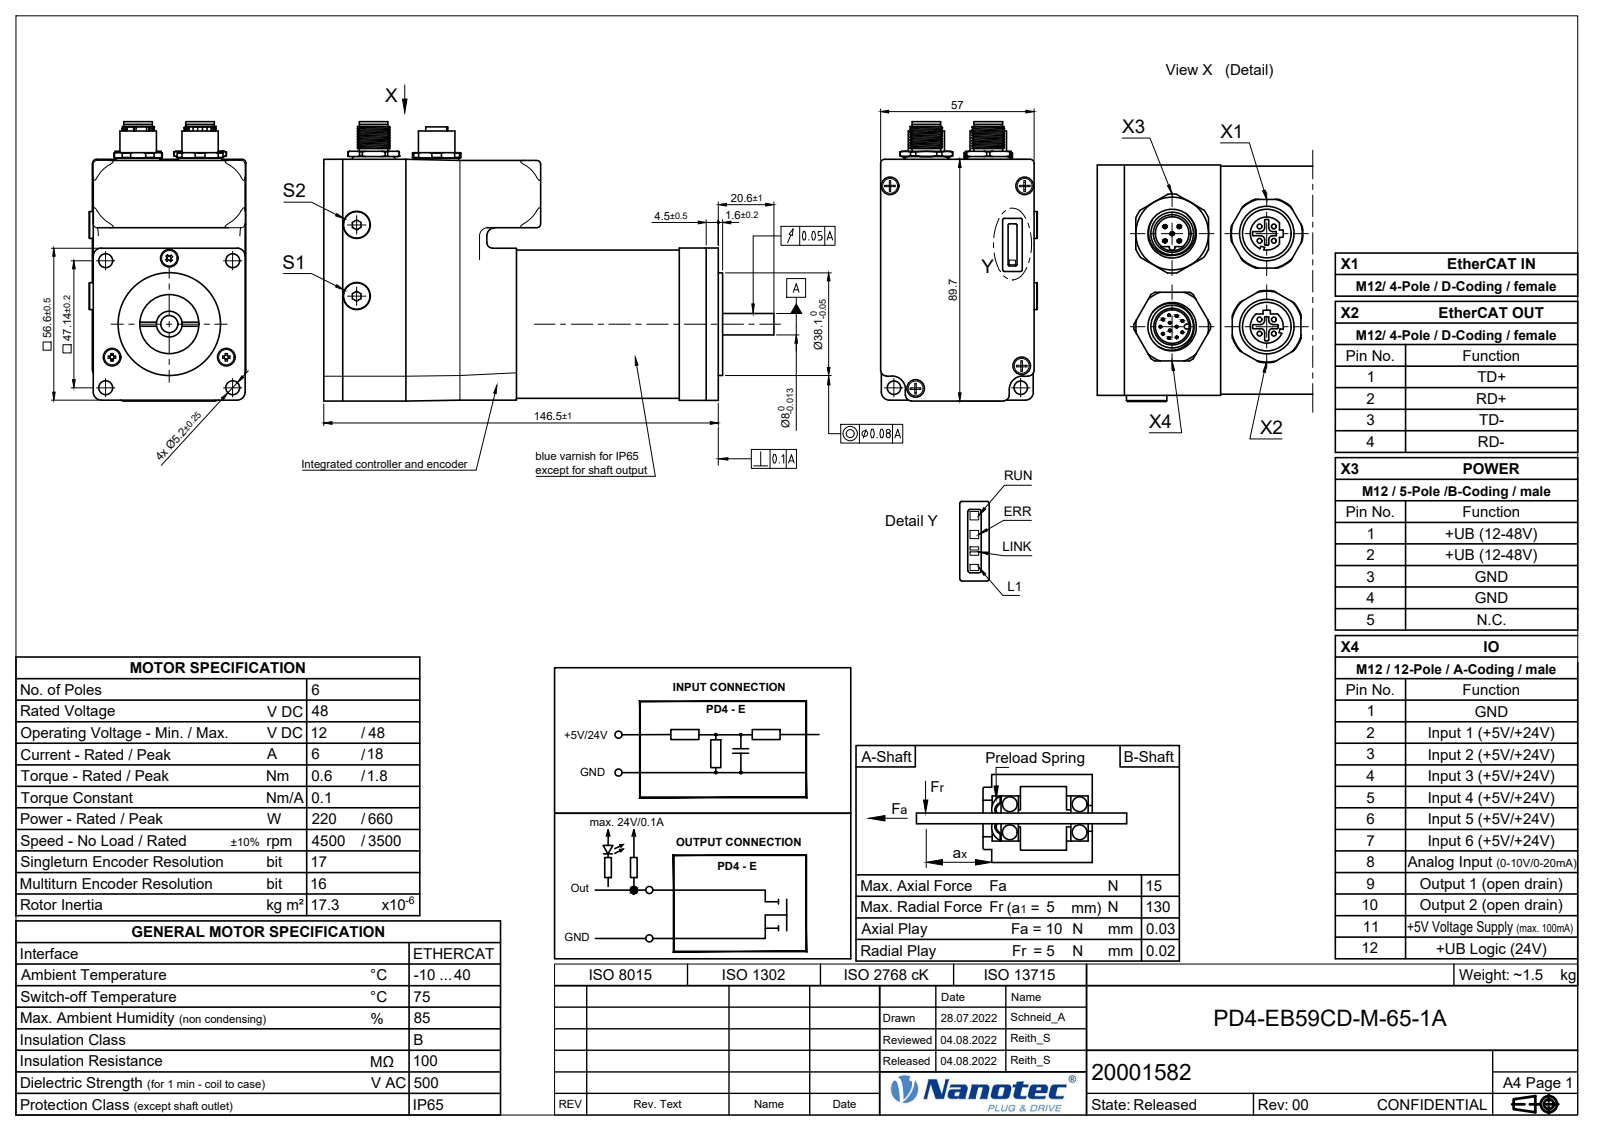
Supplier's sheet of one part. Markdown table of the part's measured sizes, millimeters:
| quantity | value |
| --- | --- |
| part name | Bauteil8 |
| STEP written by | Autodesk Inventor 2019 (AUTOMOTIVE_DESIGN) |
| units | millimeters |
| bodies | 16 solids, 1168 faces (472 planar, 381 cylindrical, 315 other) |
| overall size | 167.1 × 103.7 × 58.5 |
| volume | 346 370 mm³ |
| surface area | 93 737 mm² |
| round holes (diameter × count) | 1.2 × 8, 2.46 × 6, 3.4 × 4, 5.2 × 4, 15.3 × 4, 6.5 × 3, 11 × 3, 4.92 × 2, 12 × 2, 8.3 × 1, 10 × 1, 15.4 × 1 |
| round bosses / shafts (diameter × count) | 1 × 17, 1.6 × 13, 0.6 × 12, 5.5 × 4, 3 × 4, 2.69 × 4, 15.2 × 3, 14 × 2 |
| partial cylindrical surfaces (radius × count) | 2 × 34, 0.3 × 16, 0.2 × 12, 0.5 × 12, 1.5 × 12, 1 × 8, 3 × 7, 2.2 × 4 |
| main face-to-face distances | 63.5, 8, 2.5, 71.5, 3, 54, 2.8, 57, 1.5, 1 |
| hole center spacings | 3.53, 2.5, 23, 4.99, 21.7, 23.27, 25.22, 33.3 |
